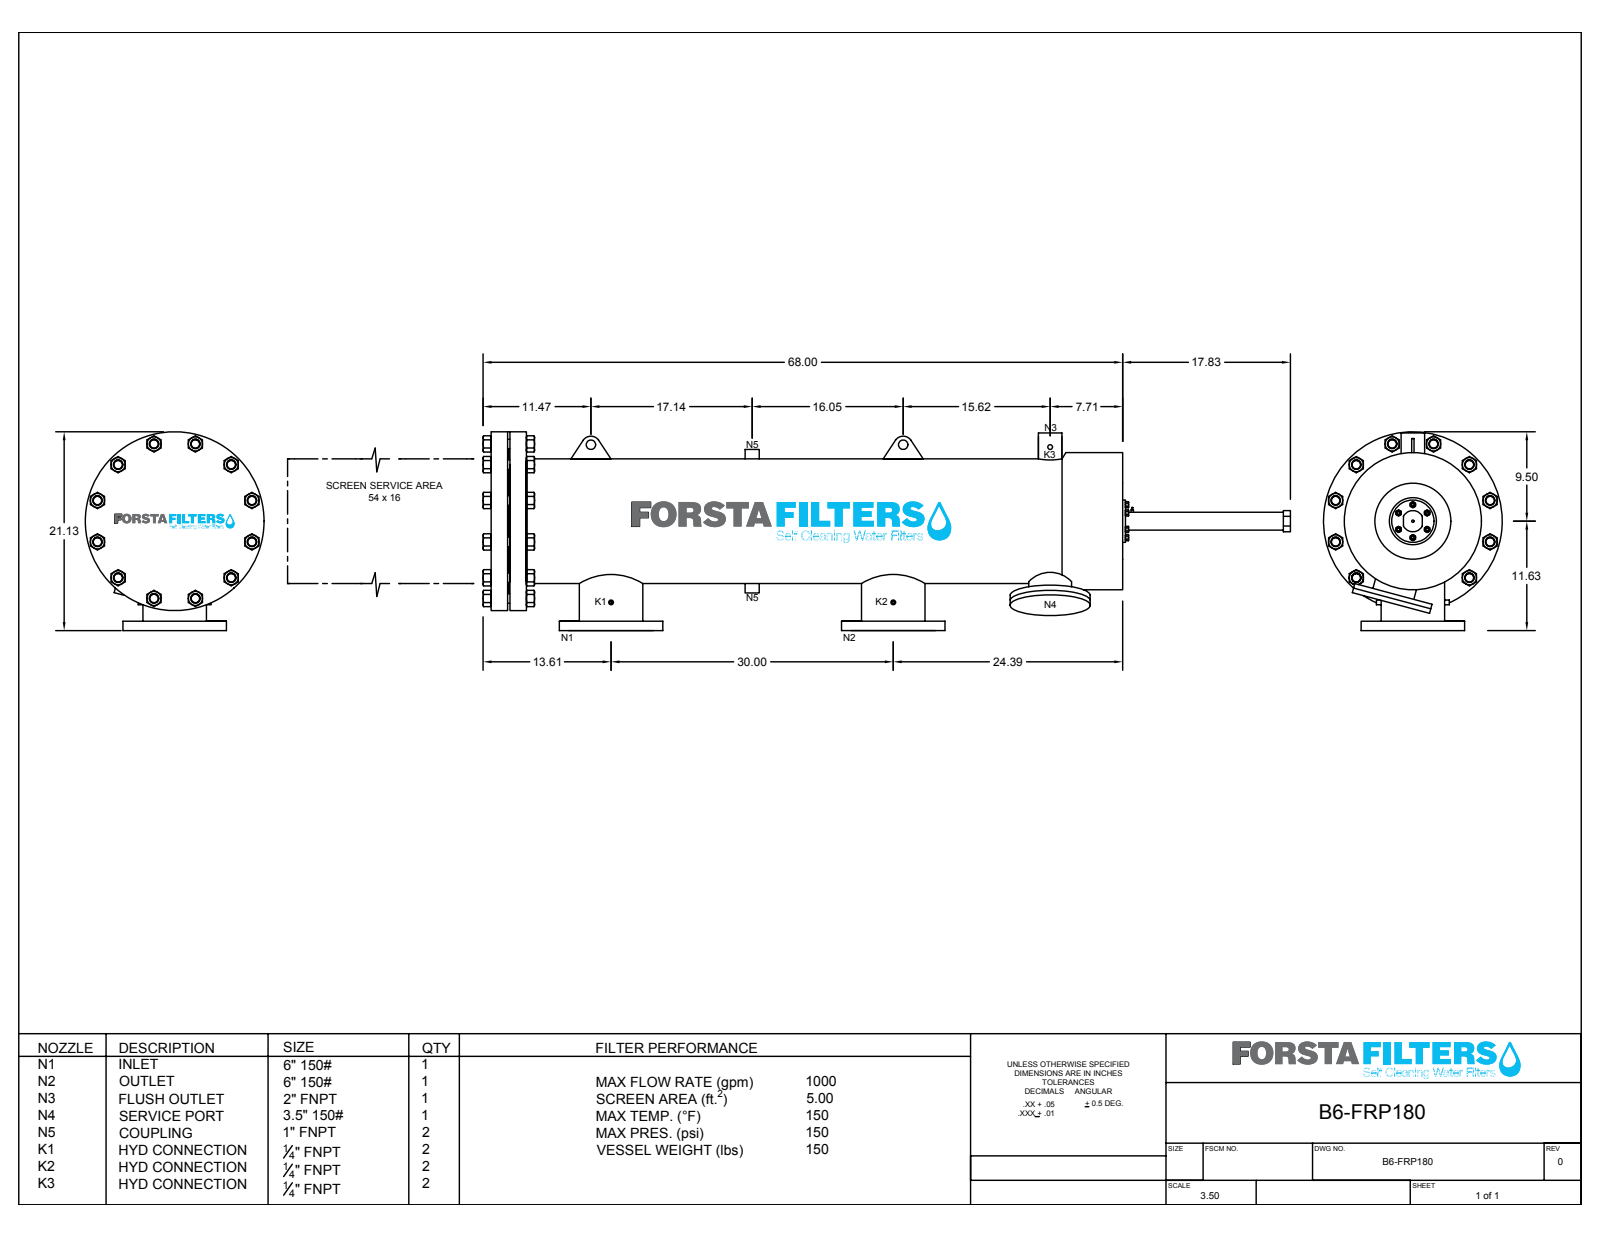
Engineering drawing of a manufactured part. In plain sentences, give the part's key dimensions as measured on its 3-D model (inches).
The part is named "B6-FRP-180". Its 3-D file was written by "SolidWorks 2018 (CONFIG_CONTROL_DESIGN)". It is 43 solids with 655 faces: 310 planar, 341 cylindrical and 4 other. Overall it measures 80.047 by 21.13 by 18.994 inches. Its volume is 1 655 cubic inches and its surface area 8 697 square inches. Round holes: 23 of diameter 0.75, 15 of diameter 1, 10 of diameter 0.375, 9 of diameter 0.88, 2 of diameter 0.246, 2 of diameter 0.25, 2 of diameter 4, 2 of diameter 6, 1 of diameter 0.375, 1 of diameter 1.505, 1 of diameter 2, 1 of diameter 12.852. Round bosses or shafts: 11 of diameter 1, 2 of diameter 11, 2 of diameter 9, 2 of diameter 6.394, 2 of diameter 4.394, 2 of diameter 0.64, 1 of diameter 18.994, 1 of diameter 14.575. Partial cylindrical surfaces (rounded edges, fillets, slot ends): 2 of radius 1, 1 of radius 1.125. The main face-to-face distances are 2, 1.75, 0.25, 0.5, 1, 63.581, 61.831, 61.581, 3.75, 59.831. The hole center spacings are 2.87, 3.75, 5.303, 6.929, 8.222, 9.112, 12.02, 16.42.
